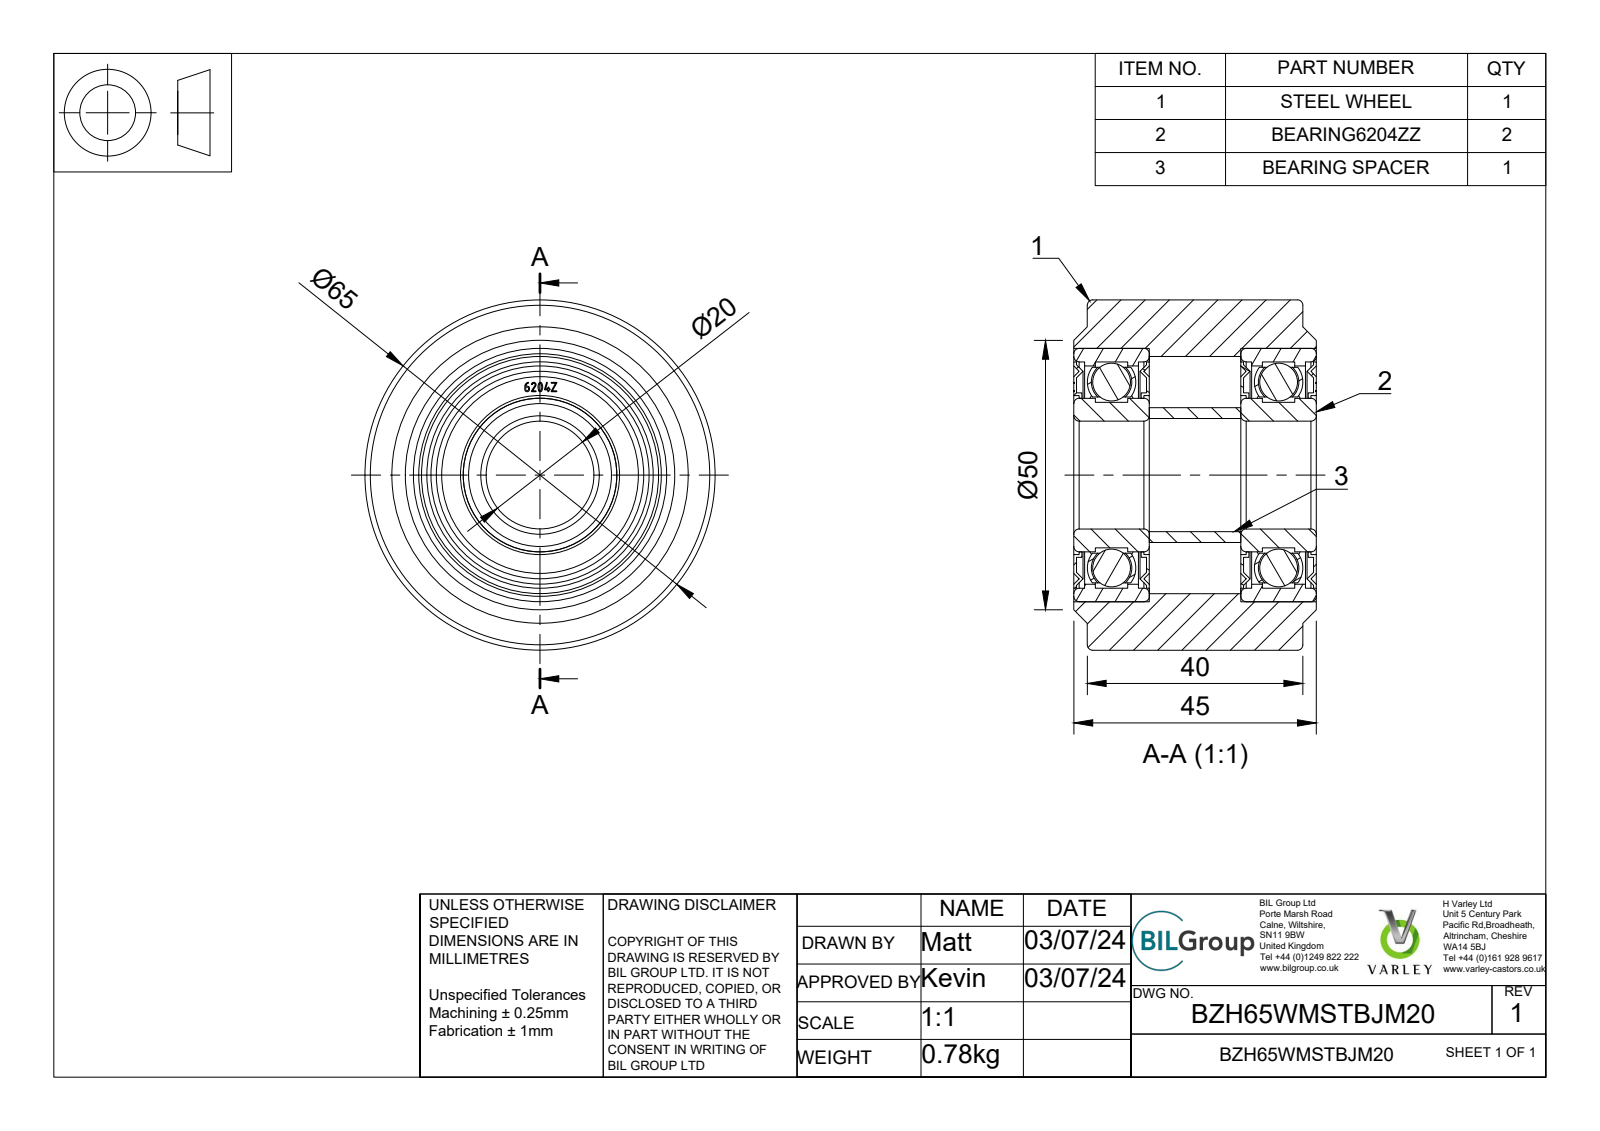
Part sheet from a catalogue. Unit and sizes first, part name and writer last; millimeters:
Units: millimetres
Overall size (bounding box): 65 × 65 × 45
Round holes (diameter × count): ⌀20 ×1, ⌀21 ×1, ⌀28.5 ×1, ⌀29.5 ×1, ⌀40.5 ×1, ⌀42 ×1, ⌀44 ×1, ⌀47 ×1
Round bosses / shafts (diameter × count): ⌀65 ×1, ⌀30.5 ×1, ⌀27 ×1, ⌀25 ×1
Partial cylindrical surfaces — rounded edges, fillets, slot ends (radius × count): R16.5 ×1, R19.5 ×1
Main face-to-face distances: 31, 14, 11.5, 42.5, 0.5, 2.5, 28.5, 13.5, 2, 29
Volume: 97 250 mm³ · Surface area: 52 667 mm²
Bodies: 28 solids, 442 faces (182 planar, 74 cylindrical, 186 other)
Part name (STEP PRODUCT): BZH65WMSTBJM20 v2; STEEL WHEEL; BEARING6204 v1; BEARING6204HT (+7 more)
STEP written by: Autodesk Translation Framework v13.14.0.145 (AUTOMOTIVE_DESIGN)
